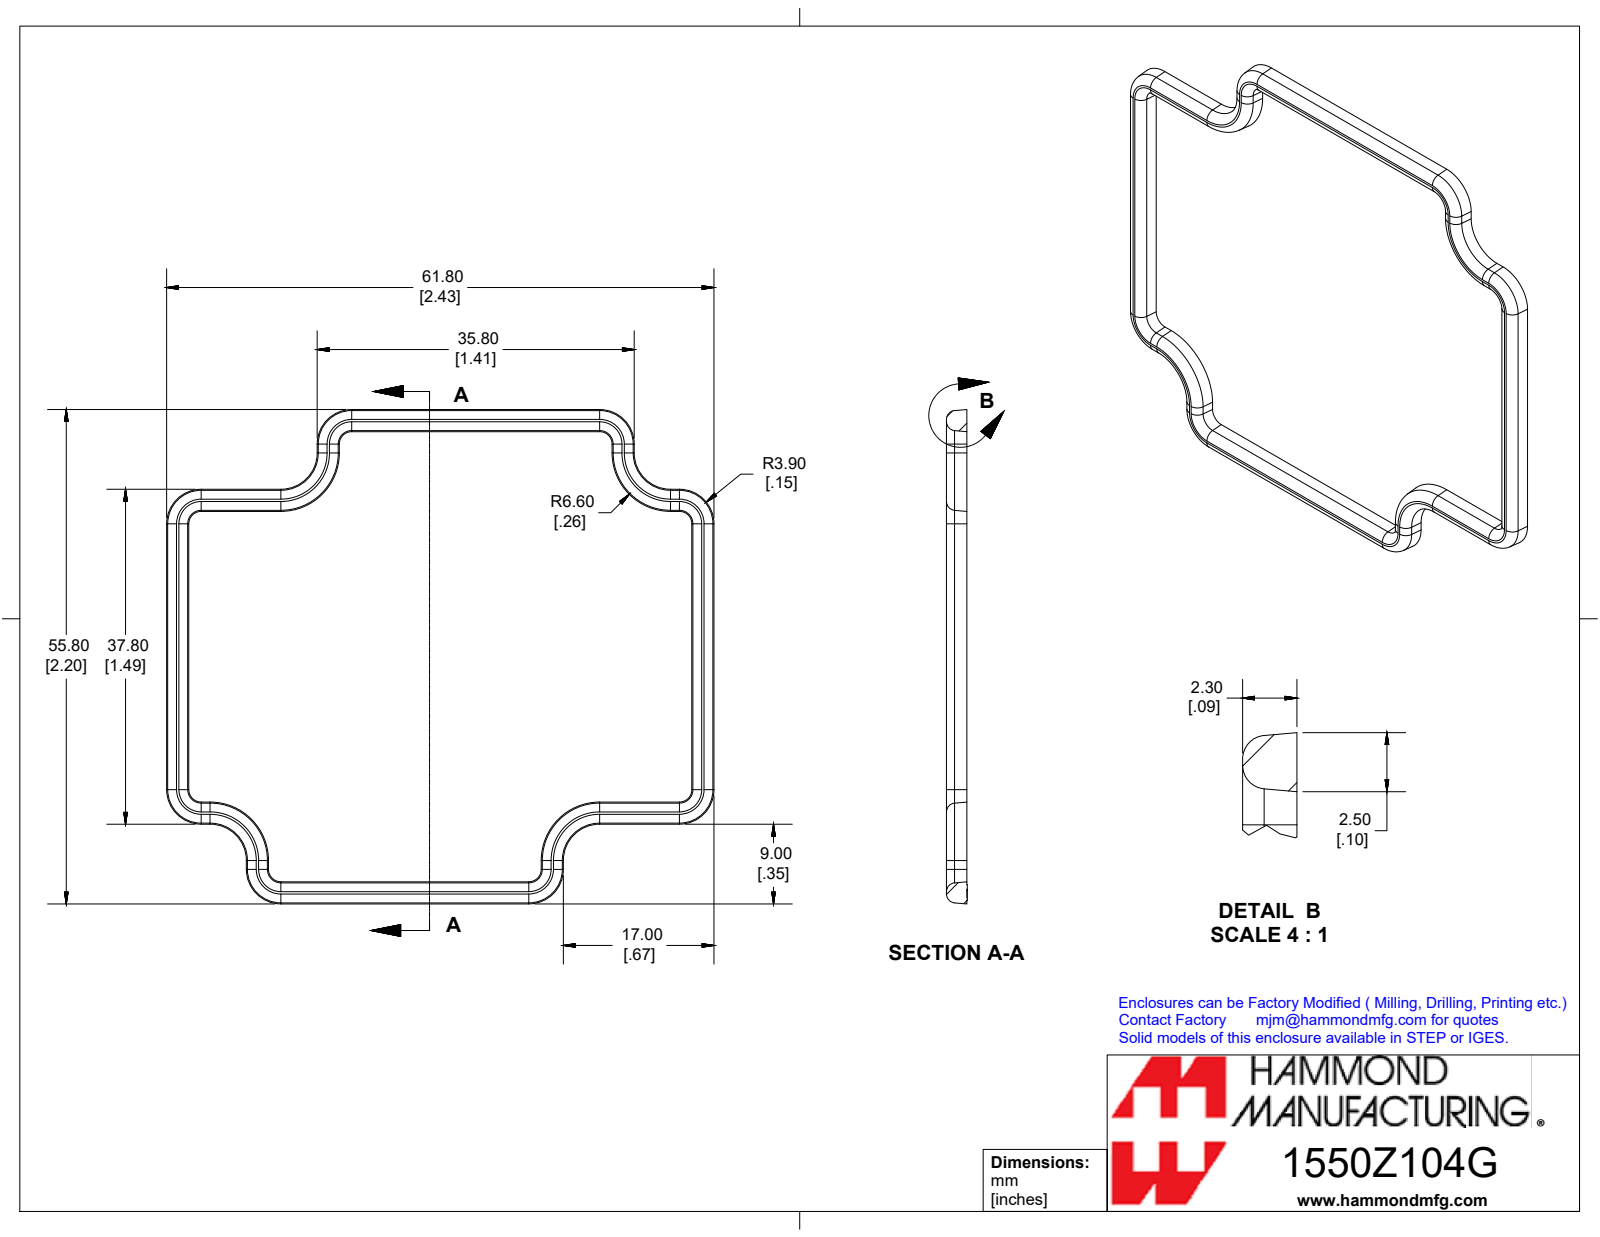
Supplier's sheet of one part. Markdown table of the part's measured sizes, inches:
| quantity | value |
| --- | --- |
| part name | 1550Z104GASKET |
| STEP written by | SolidWorks 2019 (CONFIG_CONTROL_DESIGN) |
| units | inches |
| bodies | 1 solid, 157 faces (50 planar, 24 cylindrical, 83 other) |
| overall size | 2.433 × 2.197 × 0.093 |
| volume | 0.062 in³ |
| surface area | 2.734 in² |
| partial cylindrical surfaces (radius × count) | 0.039 × 20 |
| main face-to-face distances | 2.326, 2.09, 0.353, 1.737, 0.091, 1.384, 1.972, 0.667, 1.659, 0.314 |
